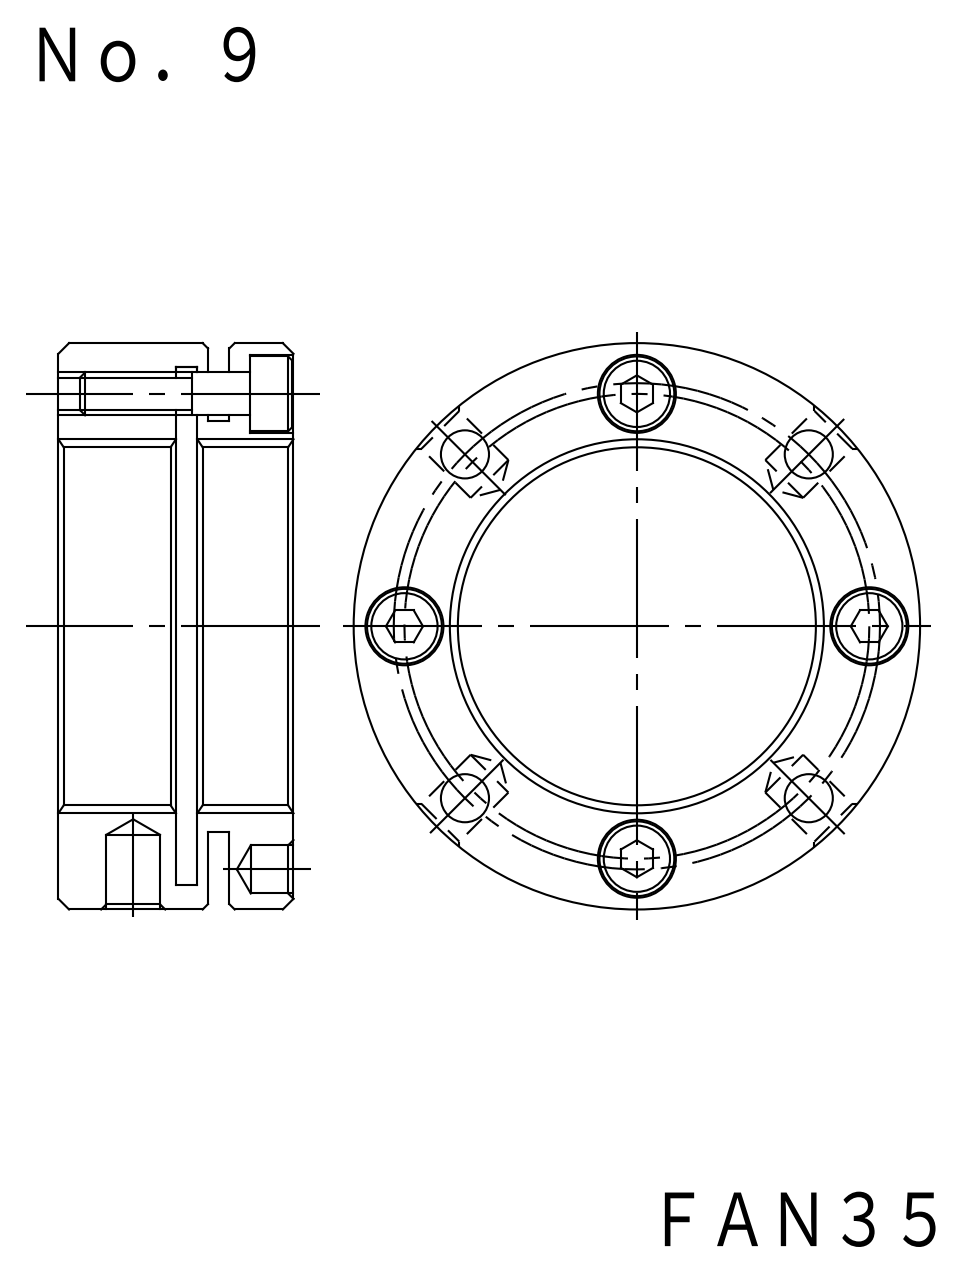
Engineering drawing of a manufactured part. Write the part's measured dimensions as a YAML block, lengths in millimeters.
part_name: "FKD FAN35; M4X16_default"
step_written_by: "SolidWorks 2012 (CONFIG_CONTROL_DESIGN)"
units: millimeters
bodies: {solids: 5, faces: 142, planar: 50, cylindrical: 76, other: 16}
overall_size: [53, 53, 22]
volume: 22857
surface_area: 15268
round_holes:
  - {diameter: 3.24, count: 4}
  - {diameter: 4.3, count: 4}
  - {diameter: 4.5, count: 4}
  - {diameter: 5, count: 4}
  - {diameter: 7.3, count: 4}
  - {diameter: 35, count: 1}
  - {diameter: 49, count: 1}
round_bosses_or_shafts:
  - {diameter: 7, count: 4}
  - {diameter: 4, count: 4}
  - {diameter: 53, count: 1}
  - {diameter: 39, count: 1}
face_to_face_distances: [2, 3, 11, 22, 16, 14, 8, 6, 5, 13]
hole_center_spacings: [17.14, 41.35, 22, 22.75, 31.11, 32.18, 44, 45.51]
